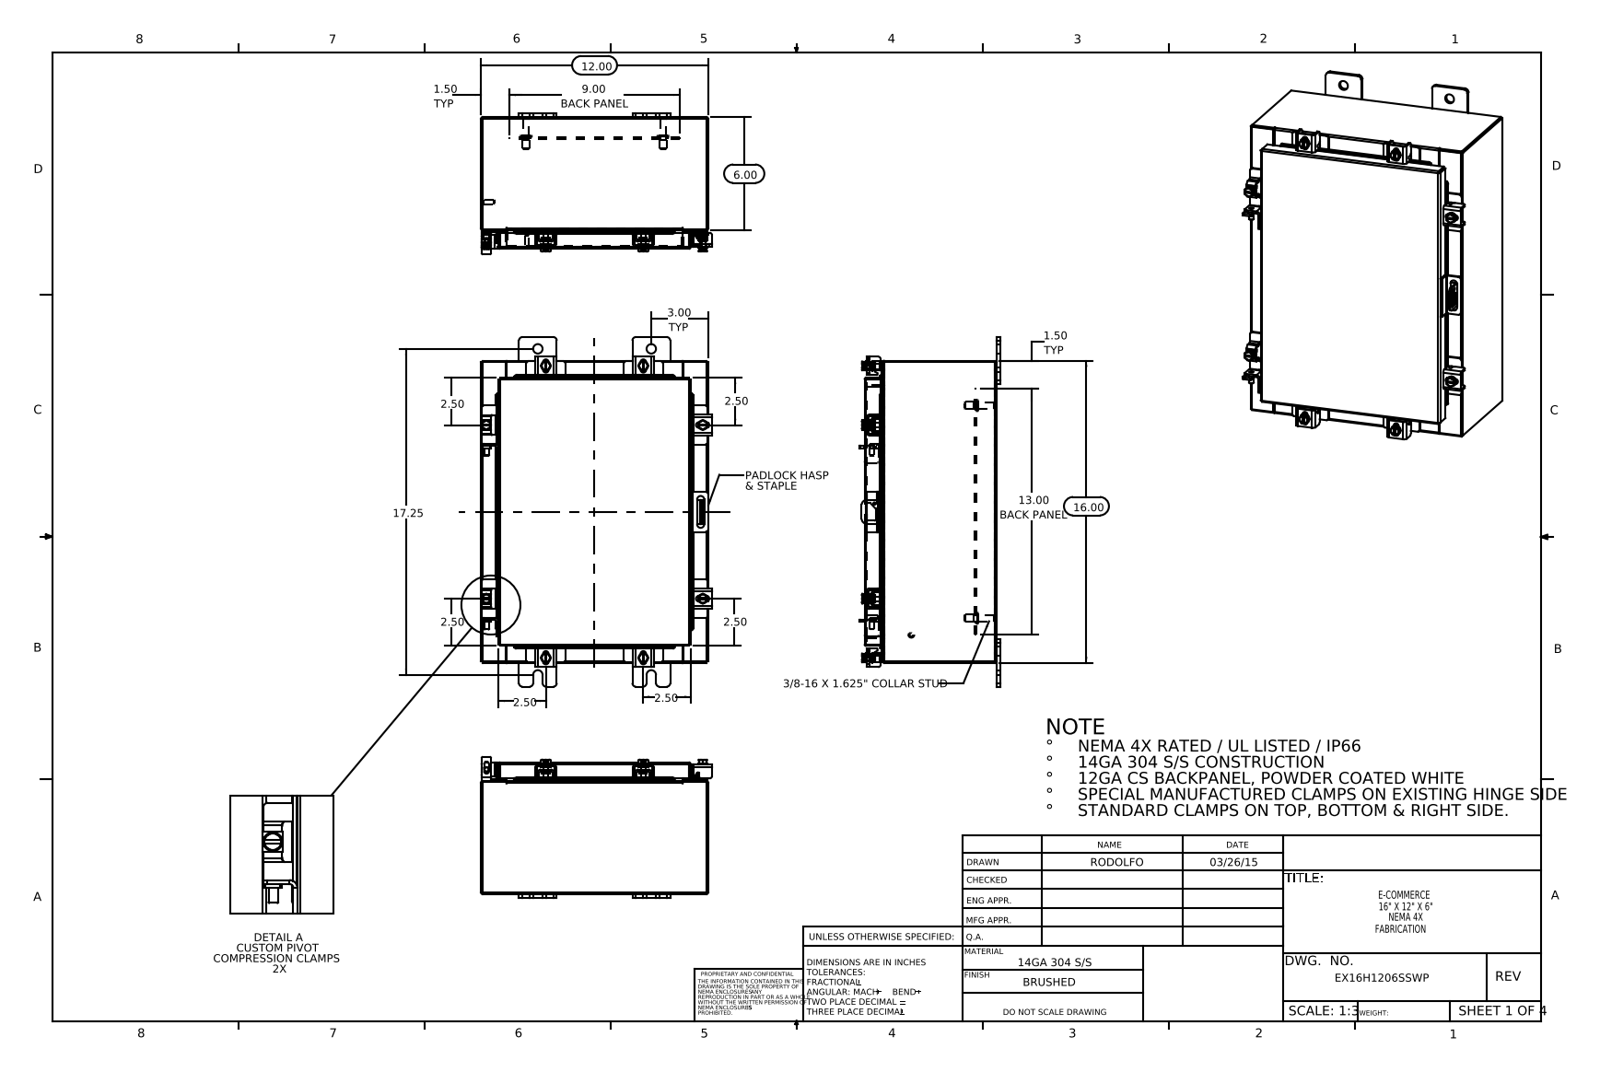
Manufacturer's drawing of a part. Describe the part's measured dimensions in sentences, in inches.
The part is named "N-WMT04X30402202210-00 22104005_DEFAULT; EX16H1206SSWP Mounting Studs; EX16H1206SSWP Padlock Hasp; EX16H1206SSWP Clamp Bracket (+8 more)". Its 3-D file was written by "SolidWorks 2014 (CONFIG_CONTROL_DESIGN)". It is 59 solids with 1468 faces: 791 planar, 549 cylindrical and 128 other. Overall it measures 18.5 by 12.211 by 7.453 inches. Its volume is 81.47 cubic inches and its surface area 2 053 square inches. Round holes: 8 of diameter 0.213, 8 of diameter 0.26, 8 of diameter 0.5, 1 of diameter 0.125, 1 of diameter 0.25. Round bosses or shafts: 8 of diameter 0.5, 8 of diameter 0.25, 6 of diameter 0.399, 4 of diameter 0.625, 4 of diameter 0.375, 4 of diameter 0.33, 2 of diameter 0.315, 2 of diameter 0.236. Partial cylindrical surfaces (rounded edges, fillets, slot ends): 34 of radius 0.06, 24 of radius 0.19, 22 of radius 0.013, 22 of radius 0.088, 16 of radius 0.1, 14 of radius 0.09, 14 of radius 0.12, 12 of radius 0.141. The main face-to-face distances are 0.075, 6.9, 11.925, 6.975, 6.826, 15.925, 5.925, 0.975, 1, 1.075. The hole center spacings are 2.347, 4.44, 8.874, 10.433, 12.715, 13.392, 13.852, 14.857.
